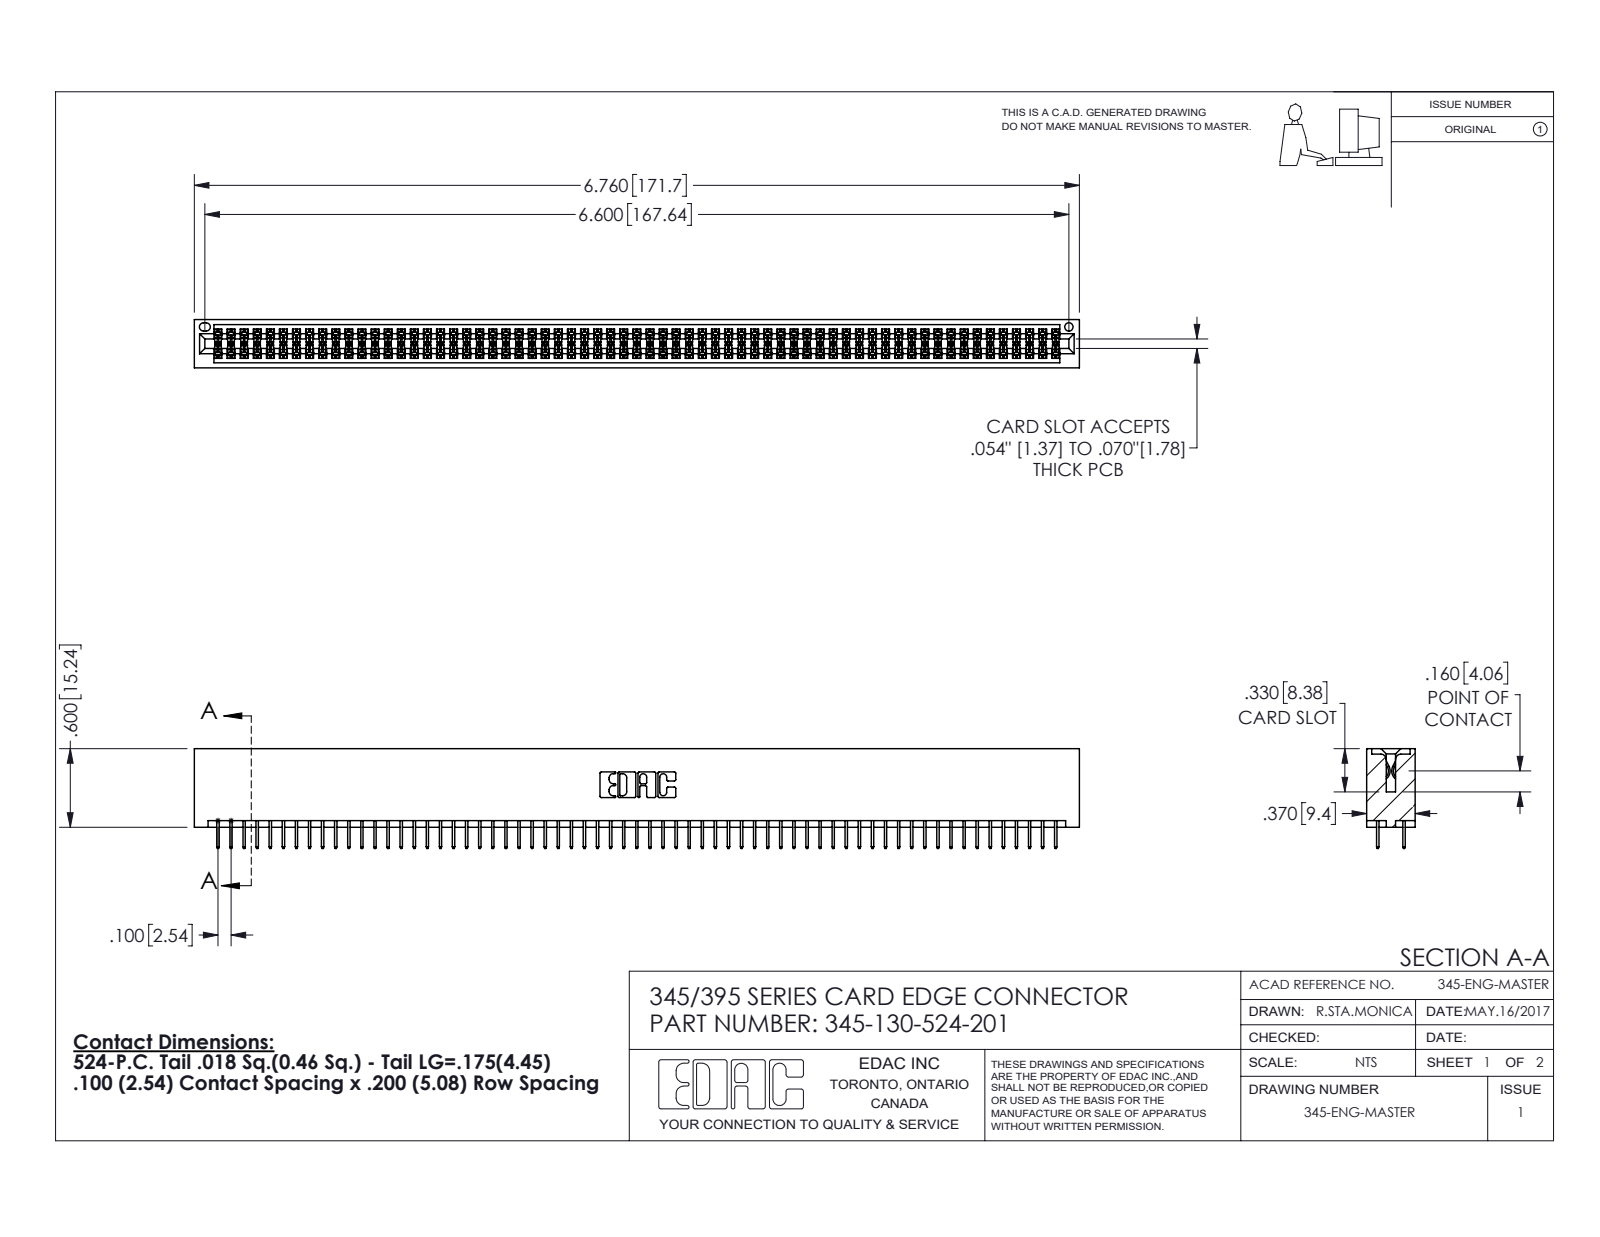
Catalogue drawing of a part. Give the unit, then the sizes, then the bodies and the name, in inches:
Units: inches
Overall size (bounding box): 6.76 × 0.762 × 0.37
Round holes (diameter × count): ⌀0.064 ×1
Partial cylindrical surfaces — rounded edges, fillets, slot ends (radius × count): R0.006 ×195, R0.01 ×22, R0.007 ×6, R0.031 ×6, R0.026 ×3, R0.014 ×2, R0.019 ×2, R0.022 ×2
Main face-to-face distances: 0.298, 0.072, 0.2, 0.37, 0.098, 0.272, 0.025, 0.225, 0.072, 0.175
Volume: 1.056 in³ · Surface area: 40.02 in²
Bodies: 131 solids, 7138 faces (5146 planar, 1992 cylindrical, 0 other)
Part name (STEP PRODUCT): 345-130-524-201; 345-292-001_345-293-124; 345 Part_No Mounting Lugs
STEP written by: SolidWorks 2016 (CONFIG_CONTROL_DESIGN)
